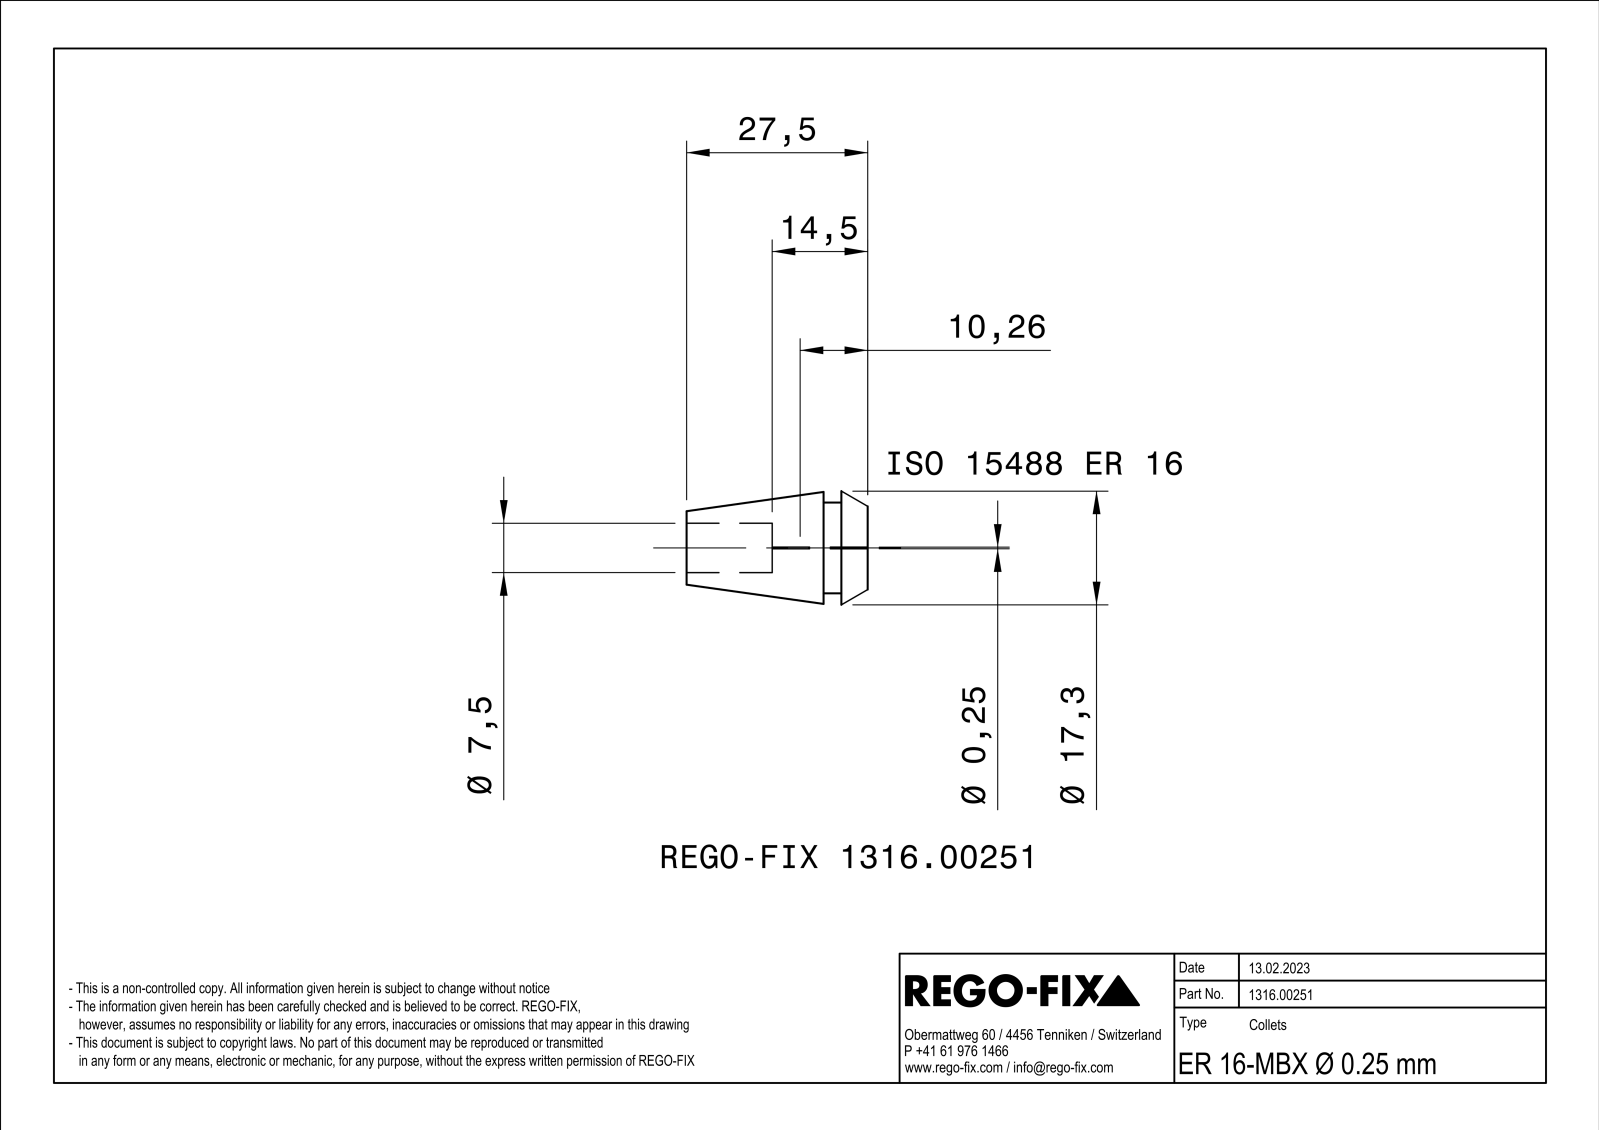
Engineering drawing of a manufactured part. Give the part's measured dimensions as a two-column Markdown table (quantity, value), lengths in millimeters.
| quantity | value |
| --- | --- |
| part name | NOCUT |
| STEP written by | SIEMENS PLM Software Solid Edge ST10 (AUTOMOTIVE_DESIGN) |
| units | millimeters |
| bodies | 1 solid, 109 faces (36 planar, 27 cylindrical, 46 other) |
| overall size | 27.5 × 16.91 × 16.9 |
| volume | 3 347 mm³ |
| surface area | 3 341 mm² |
| round holes (diameter × count) | 2 × 3, 7.5 × 1 |
| round bosses / shafts (diameter × count) | 13.8 × 1 |
| partial cylindrical surfaces (radius × count) | 25 × 3, 0.12 × 1 |
| main face-to-face distances | 0.34, 0.46, 0.8, 6.7, 4, 2.7, 27.5, 23.5, 20.8, 14.5 |
| hole center spacings | 2.1, 3.64 |
